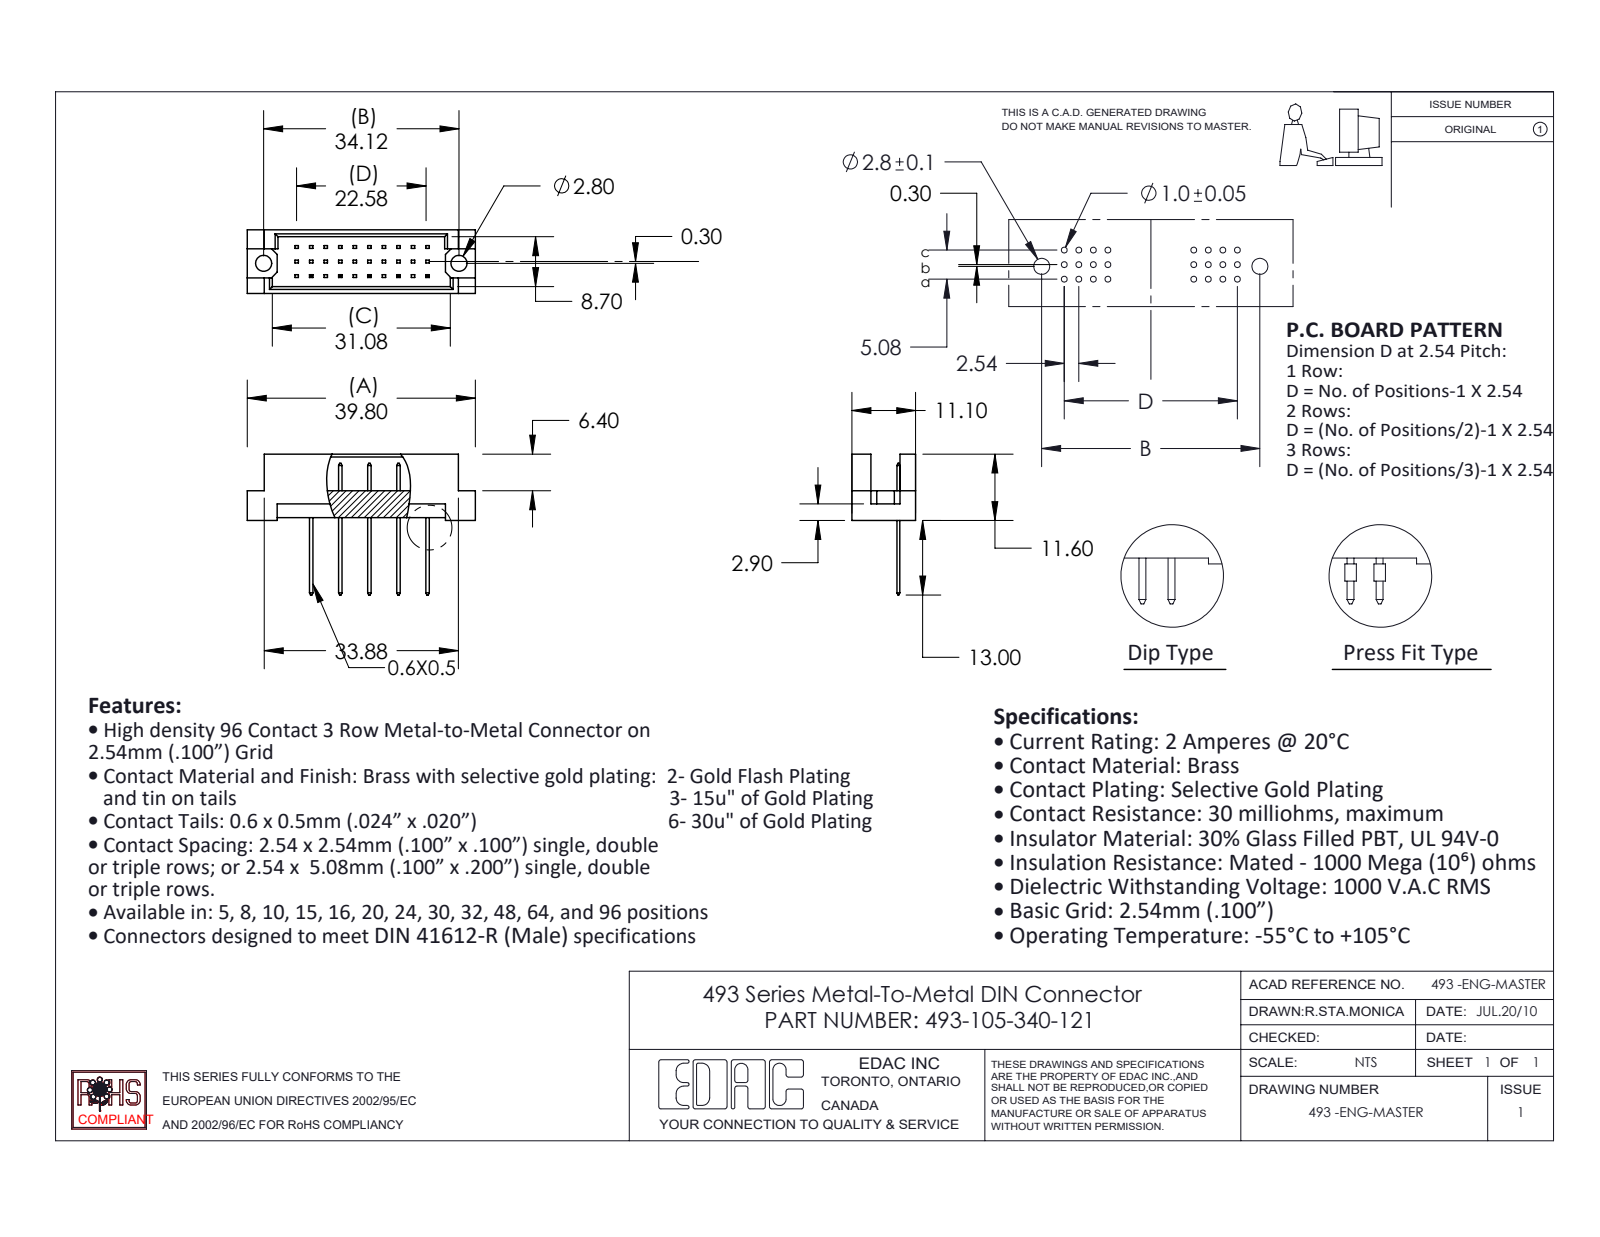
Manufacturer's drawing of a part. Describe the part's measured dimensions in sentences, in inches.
The part is named "493-290_40; 493 Part_30; 493-105-340-121". Its 3-D file was written by "SolidWorks 2020 (CONFIG_CONTROL_DESIGN)". It is 6 solids with 242 faces: 238 planar, 4 cylindrical and 0 other. Overall it measures 1.567 by 0.969 by 0.437 inches. Its volume is 0.147 cubic inches and its surface area 4.633 square inches. Round holes: 2 of diameter 0.11. The main face-to-face distances are 0.047, 0.39, 0.437, 0.343, 0.02, 0.185, 0.2, 0.094, 0.109, 0.128. The hole center spacings are 1.343.
